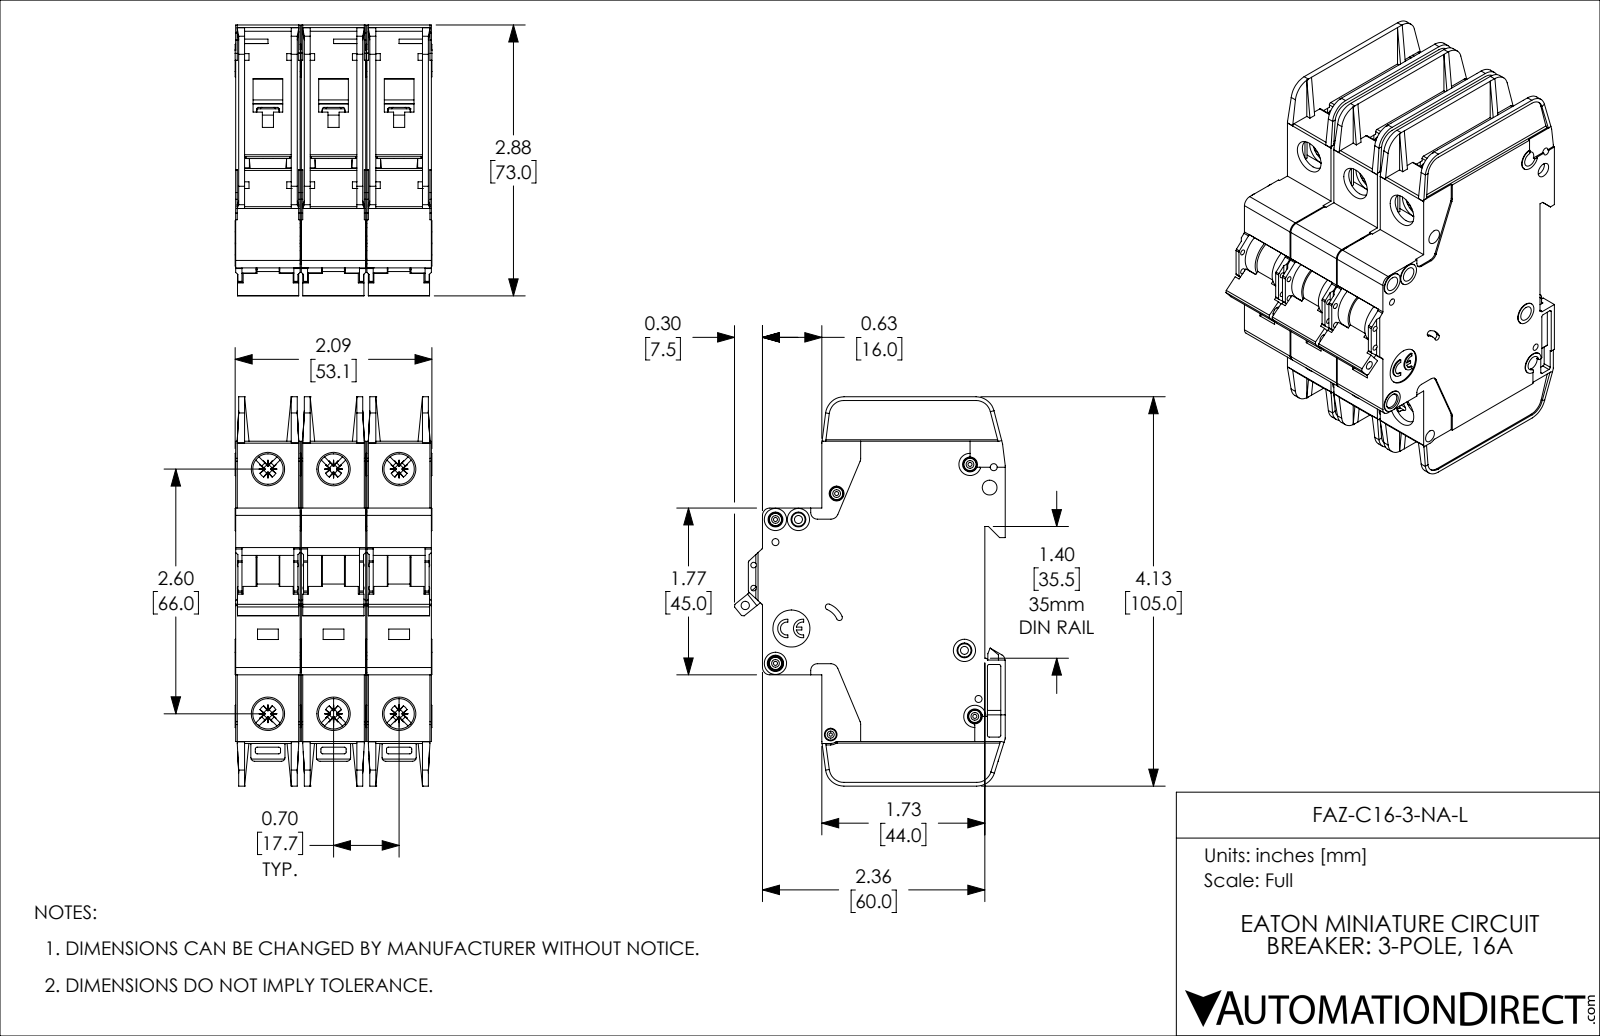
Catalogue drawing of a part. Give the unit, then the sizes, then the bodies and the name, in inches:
Units: inches
Overall size (bounding box): 4.134 × 2.876 × 2.091
Round holes (diameter × count): ⌀0.157 ×8, ⌀0.323 ×6, ⌀0.043 ×5, ⌀0.075 ×4, ⌀0.059 ×2, ⌀0.085 ×2, ⌀0.035 ×1, ⌀0.089 ×1, ⌀0.098 ×1, ⌀0.134 ×1, ⌀0.394 ×1
Round bosses / shafts (diameter × count): ⌀0.13 ×5, ⌀0.236 ×4, ⌀0.118 ×4, ⌀0.098 ×3
Partial cylindrical surfaces — rounded edges, fillets, slot ends (radius × count): R0.02 ×72, R0.016 ×30, R0.039 ×18, R0.043 ×12, R0.079 ×12, R0.008 ×6, R0.01 ×6, R0.028 ×6
Main face-to-face distances: 0.697, 0.047, 1.394, 0.685, 0.591, 1.382, 0.744, 0.65, 0.106, 0.094
Hole centre spacings: 0.697, 2.69, 2.598, 0.244, 0.537, 0.87, 1.394, 2.948
Volume: 14.05 in³ · Surface area: 123 in²
Bodies: 3 solids, 3381 faces (2013 planar, 1071 cylindrical, 297 other)
Part name (STEP PRODUCT): FAZ-C16-3-NA-L
STEP written by: SolidWorks 2019 (AUTOMOTIVE_DESIGN)
